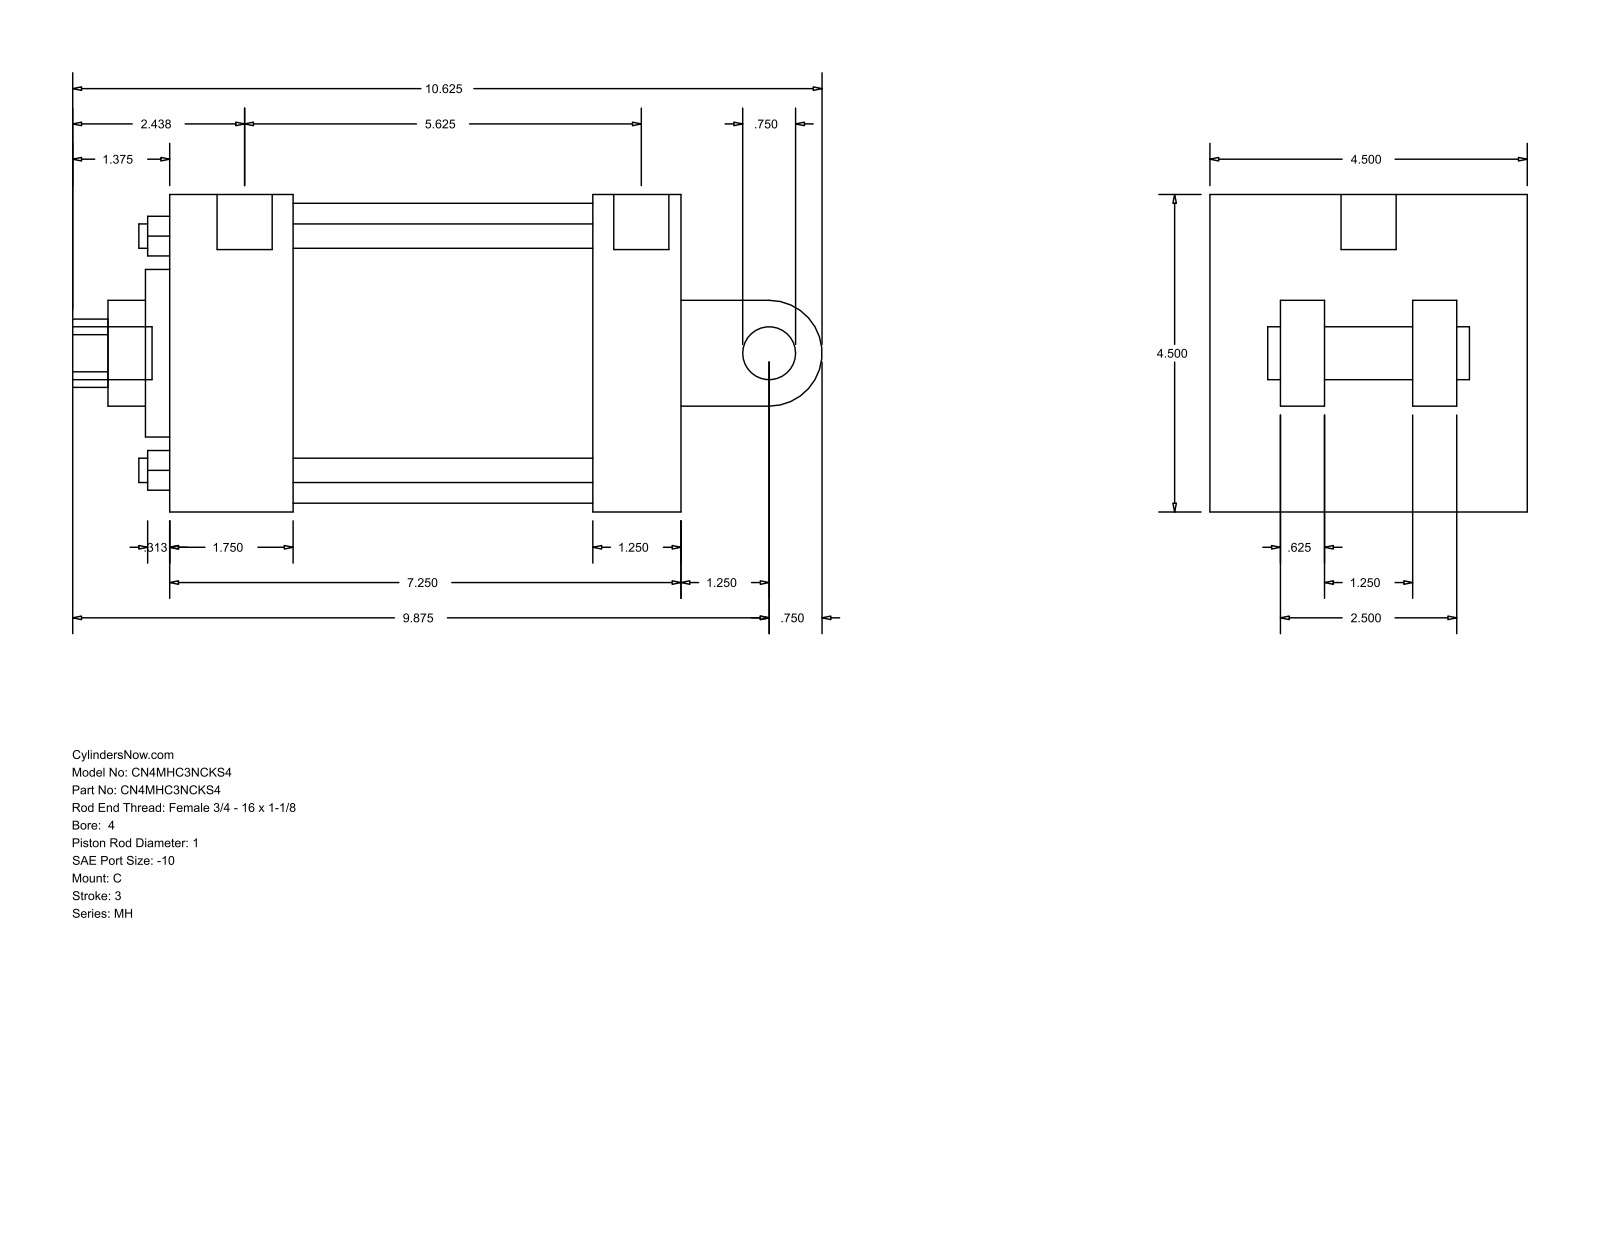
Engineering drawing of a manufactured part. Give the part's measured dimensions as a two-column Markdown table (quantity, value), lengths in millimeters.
| quantity | value |
| --- | --- |
| part name | MH_C__0400_1 |
| STEP written by | GSSL Pune (CONFIG_CONTROL_DESIGN) |
| units | millimeters |
| bodies | 0 solids, 101 faces (71 planar, 30 cylindrical, 0 other) |
| overall size | 269.88 × 114.3 × 114.3 |
| round holes (diameter × count) | 8.76 × 4, 8.73 × 2, 19.84 × 1, 25.4 × 1, 38.1 × 1, 60.33 × 1, 107.95 × 1 |
| round bosses / shafts (diameter × count) | 19.05 × 2, 8.73 × 2, 19.84 × 1 |
| partial cylindrical surfaces (radius × count) | 12.29 × 1, 19.05 × 1 |
| main face-to-face distances | 114.3, 184.15, 44.46, 152.4, 107.94, 139.69, 31.75, 73.03, 15.87, 47.63 |
| hole center spacings | 59.62, 84.32, 119.25, 1.59 |
